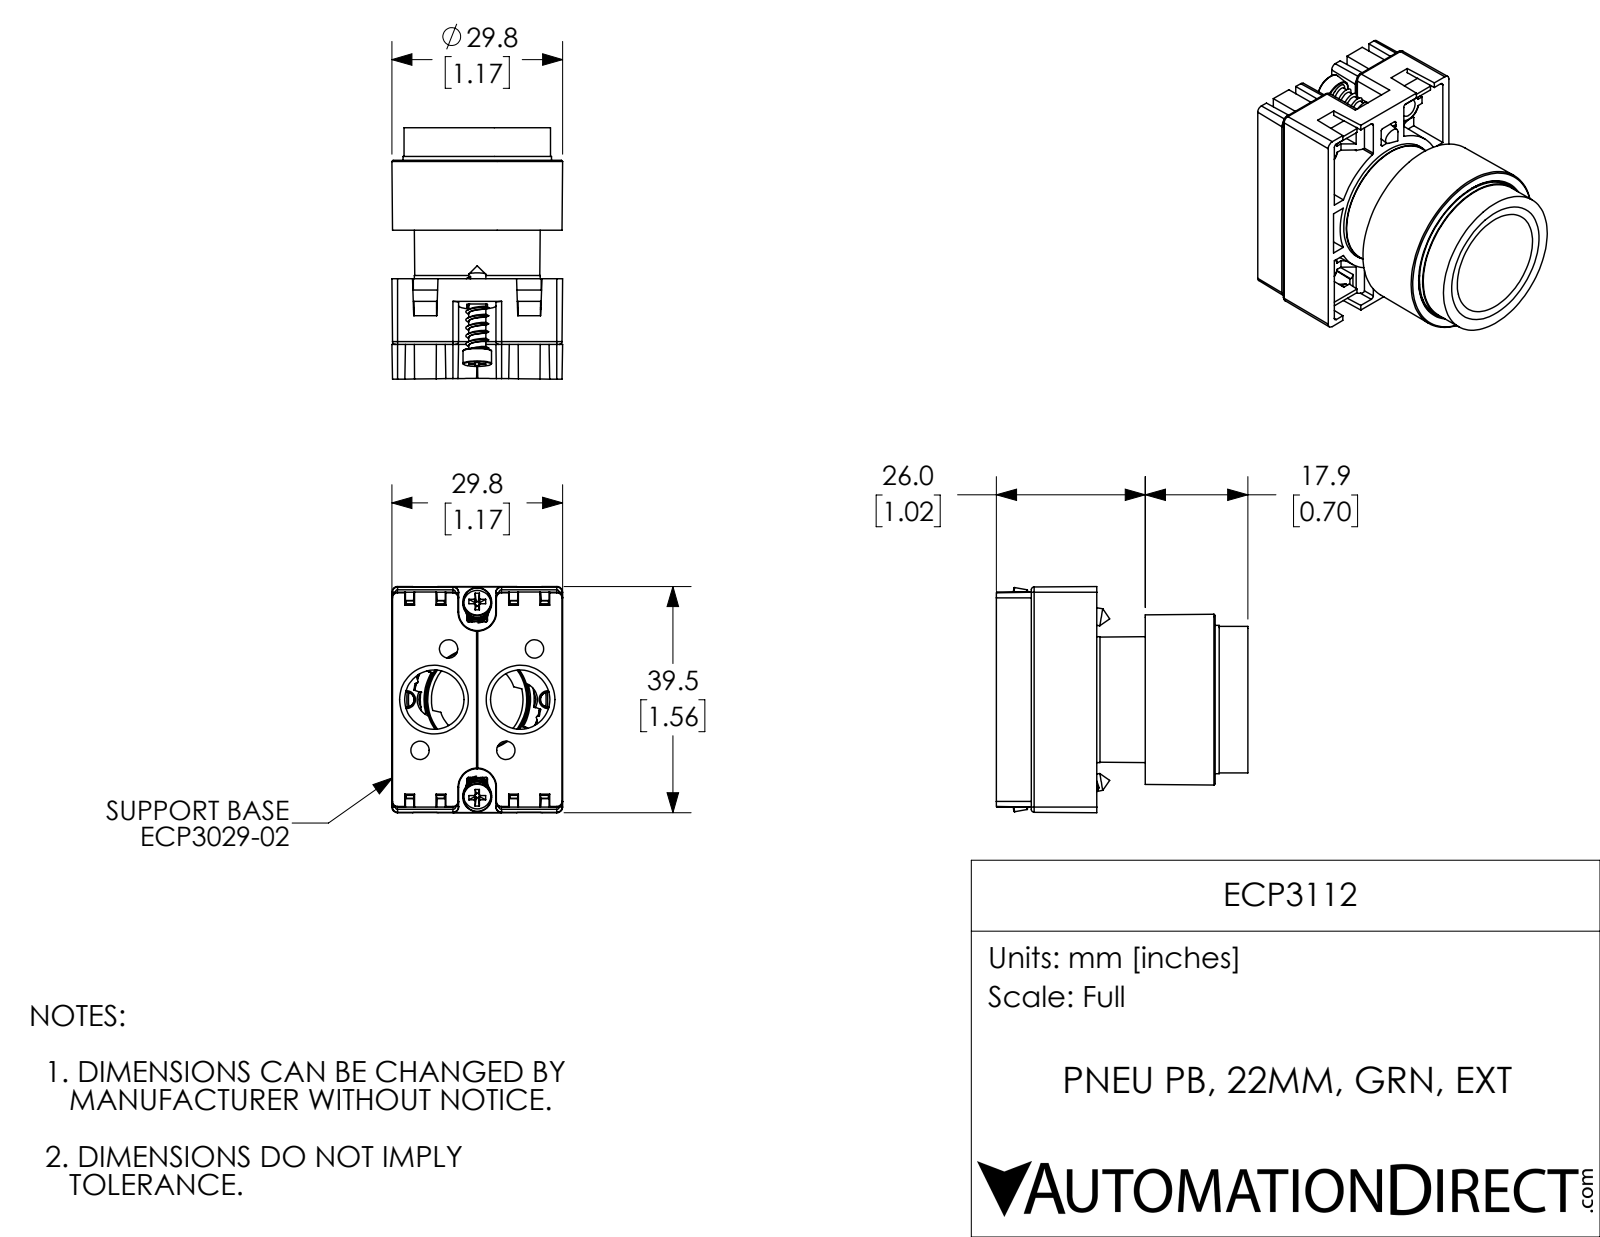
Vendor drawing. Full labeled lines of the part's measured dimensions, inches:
Part name (STEP PRODUCT): ECP3112
STEP written by: SolidWorks 2017 (AUTOMOTIVE_DESIGN)
Units: inches
Bodies: 7 solids, 781 faces (364 planar, 133 cylindrical, 284 other)
Overall size (bounding box): 1.728 × 1.555 × 1.173
Volume: 1.025 in³ · Surface area: 29.57 in²
Round holes (diameter × count): ⌀0.081 ×4, ⌀0.407 ×2, ⌀0.697 ×1, ⌀0.732 ×1
Round bosses / shafts (diameter × count): ⌀0.197 ×2, ⌀0.118 ×2, ⌀1.02 ×1, ⌀1.008 ×1, ⌀0.866 ×1
Partial cylindrical surfaces — rounded edges, fillets, slot ends (radius × count): R0.02 ×18, R0.006 ×8, R0.012 ×8, R0.008 ×4, R0.039 ×4, R0.008 ×2, R0.118 ×2, R0.128 ×2
Main face-to-face distances: 1.261, 0.177, 0.067, 0.715, 0.962, 0.811, 0.451, 0.587, 0.528, 0.519
Hole centre spacings: 0.304, 0.541, 0.817, 0.295, 0.472, 0.972, 1.081, 0.591
